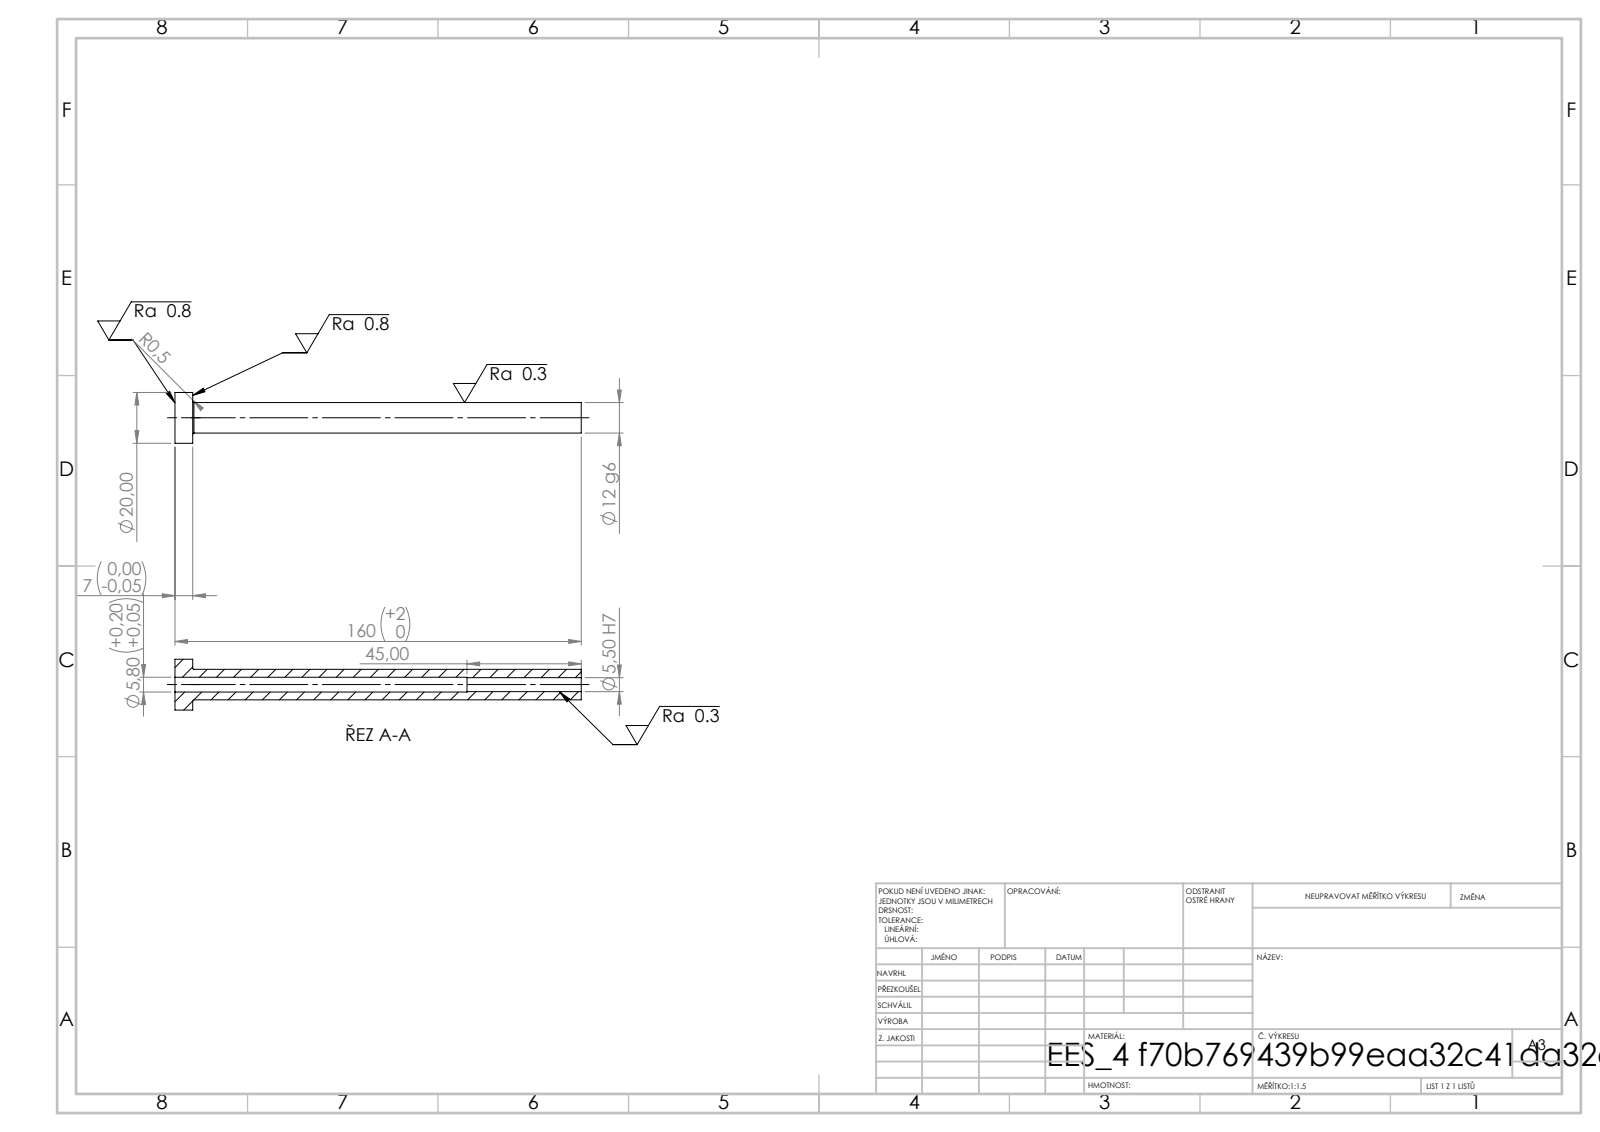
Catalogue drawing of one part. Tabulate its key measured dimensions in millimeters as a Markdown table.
| quantity | value |
| --- | --- |
| STEP written by | SolidWorks 2019 (CONFIG_CONTROL_DESIGN) |
| units | millimeters |
| bodies | 1 solid, 14 faces (4 planar, 8 cylindrical, 2 other) |
| overall size | 160 × 20 × 20 |
| volume | 15 398 mm³ |
| surface area | 9 654 mm² |
| round holes (diameter × count) | 5.5 × 1, 5.8 × 1 |
| round bosses / shafts (diameter × count) | 20 × 1, 12 × 1 |
| main face-to-face distances | 7, 160, 153, 115, 108, 45 |
